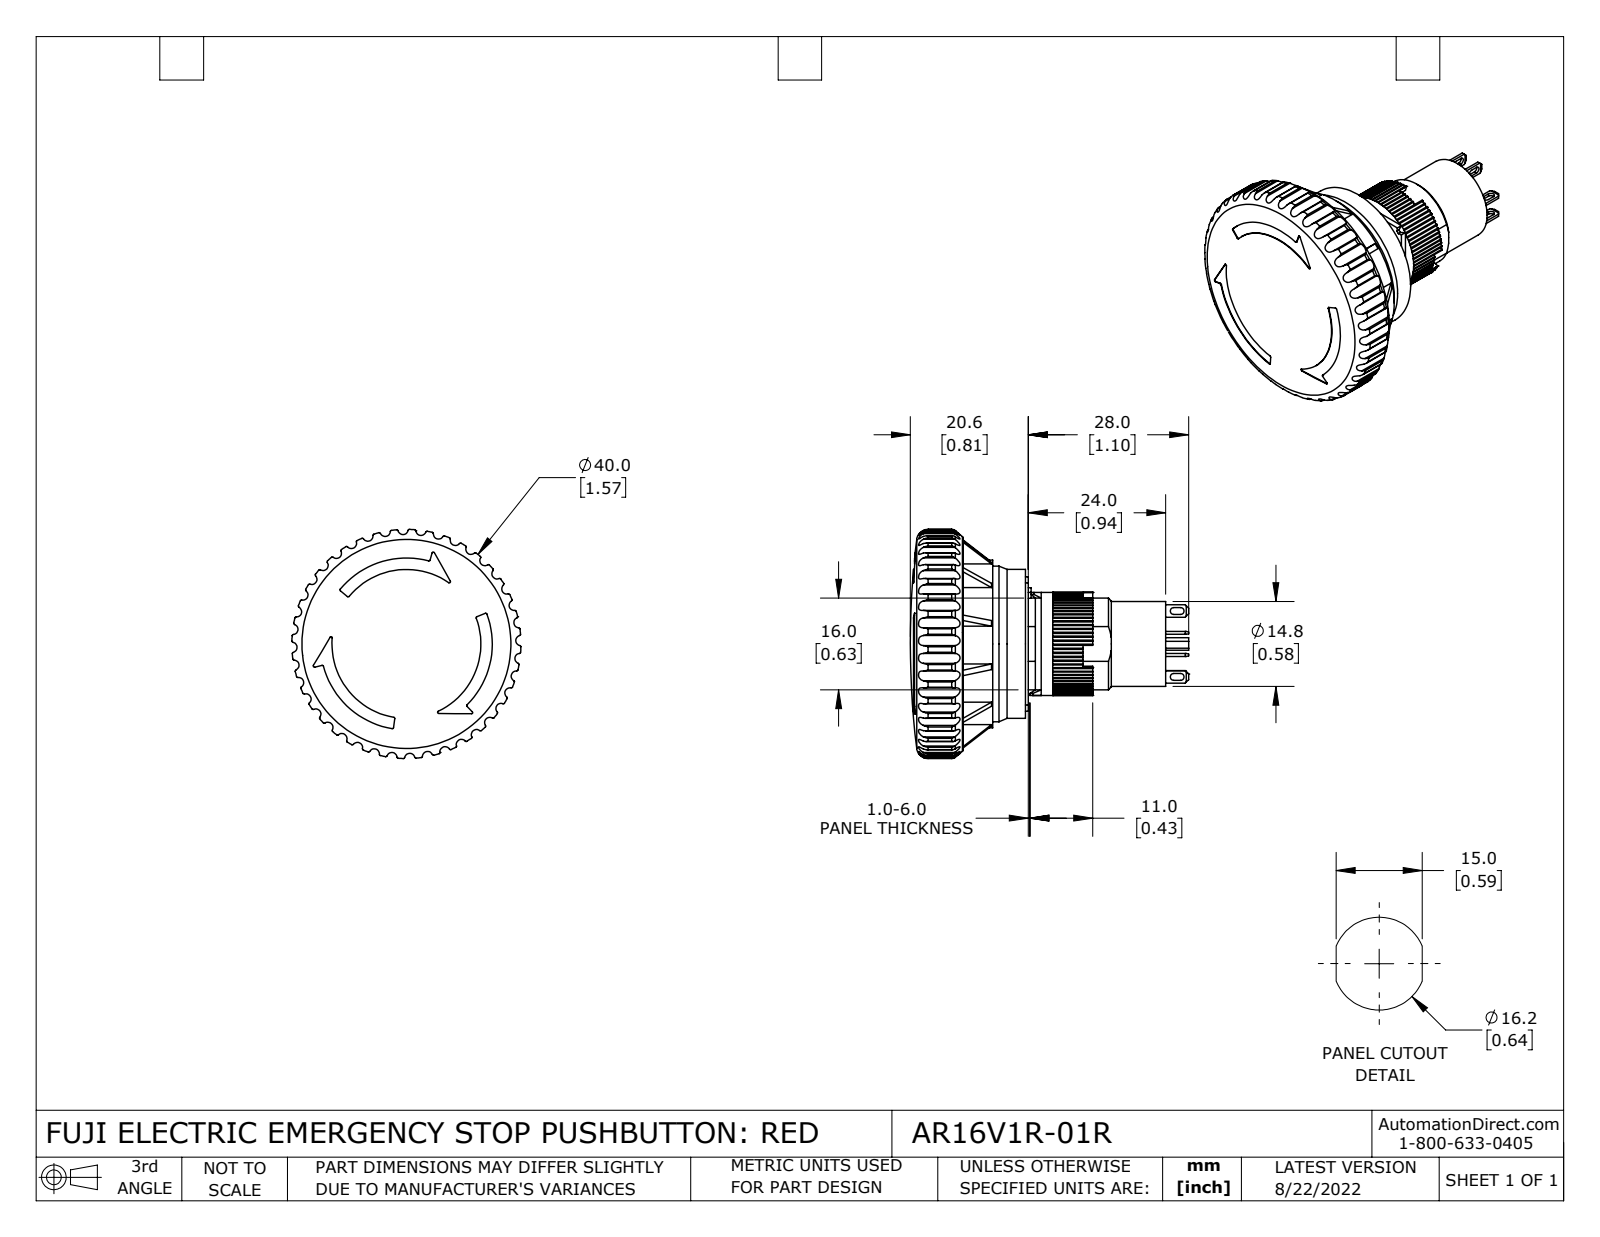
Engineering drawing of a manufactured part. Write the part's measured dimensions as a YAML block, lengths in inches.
part_name: "AR16V1R-01R"
step_written_by: "SolidWorks 2021 (CONFIG_CONTROL_DESIGN)"
units: inches
bodies: {solids: 5, faces: 1001, planar: 495, cylindrical: 410, other: 96}
overall_size: [1.913, 1.575, 1.575]
volume: 0.963
surface_area: 19.04
round_holes:
  - {diameter: 0.583, count: 1}
  - {diameter: 0.63, count: 1}
  - {diameter: 0.709, count: 1}
  - {diameter: 1.069, count: 1}
  - {diameter: 1.433, count: 1}
round_bosses_or_shafts:
  - {diameter: 1.154, count: 1}
  - {diameter: 1.024, count: 1}
  - {diameter: 0.858, count: 1}
  - {diameter: 0.236, count: 1}
partial_cylinders:
  - {radius: 0.008, count: 80}
  - {radius: 0.01, count: 80}
  - {radius: 0.035, count: 40}
  - {radius: 0.02, count: 8}
  - {radius: 0.024, count: 8}
  - {radius: 0.039, count: 2}
  - {radius: 0.031, count: 1}
  - {radius: 0.114, count: 1}
face_to_face_distances: [0.039, 0.421, 0.53, 0.108, 0.02, 0.069, 0.856, 0.49, 0.089, 0.049]
